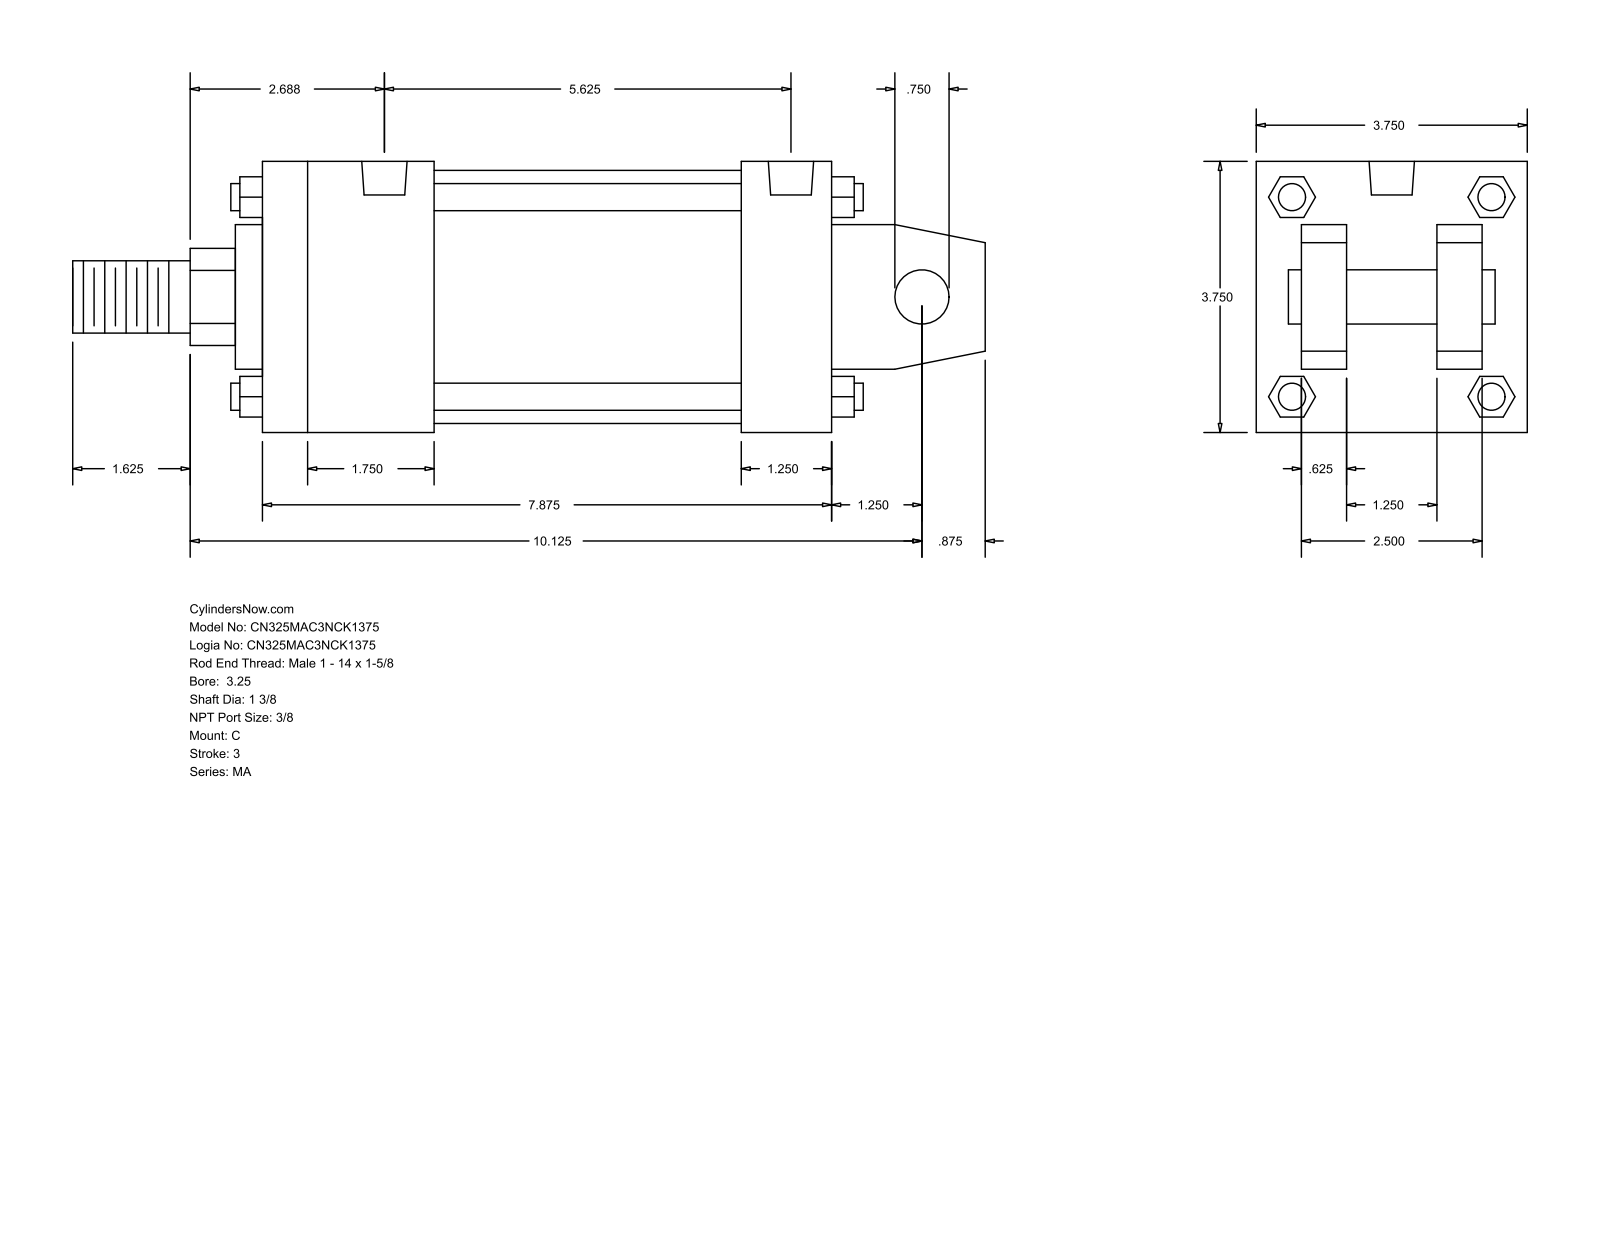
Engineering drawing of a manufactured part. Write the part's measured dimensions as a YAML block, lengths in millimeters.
part_name: "MA_C__0325_1.375"
step_written_by: "GSSL Pune (CONFIG_CONTROL_DESIGN)"
units: millimeters
bodies: {solids: 0, faces: 139, planar: 108, cylindrical: 31, other: 0}
overall_size: [320.68, 95.25, 95.25]
round_holes:
  - {diameter: 11.11, count: 4}
  - {diameter: 15.93, count: 2}
round_bosses_or_shafts:
  - {diameter: 9.53, count: 4}
  - {diameter: 88.9, count: 1}
  - {diameter: 50.8, count: 1}
  - {diameter: 34.92, count: 1}
  - {diameter: 25.4, count: 1}
  - {diameter: 19.05, count: 1}
partial_cylinders:
  - {radius: 17.06, count: 1}
face_to_face_distances: [95.24, 15.87, 63.5, 200.03, 31.74, 79.37, 47.63, 168.28, 31.75, 60.32]
hole_center_spacings: [133.35, 4.76, 4.77, 138.11, 138.12, 142.88]
